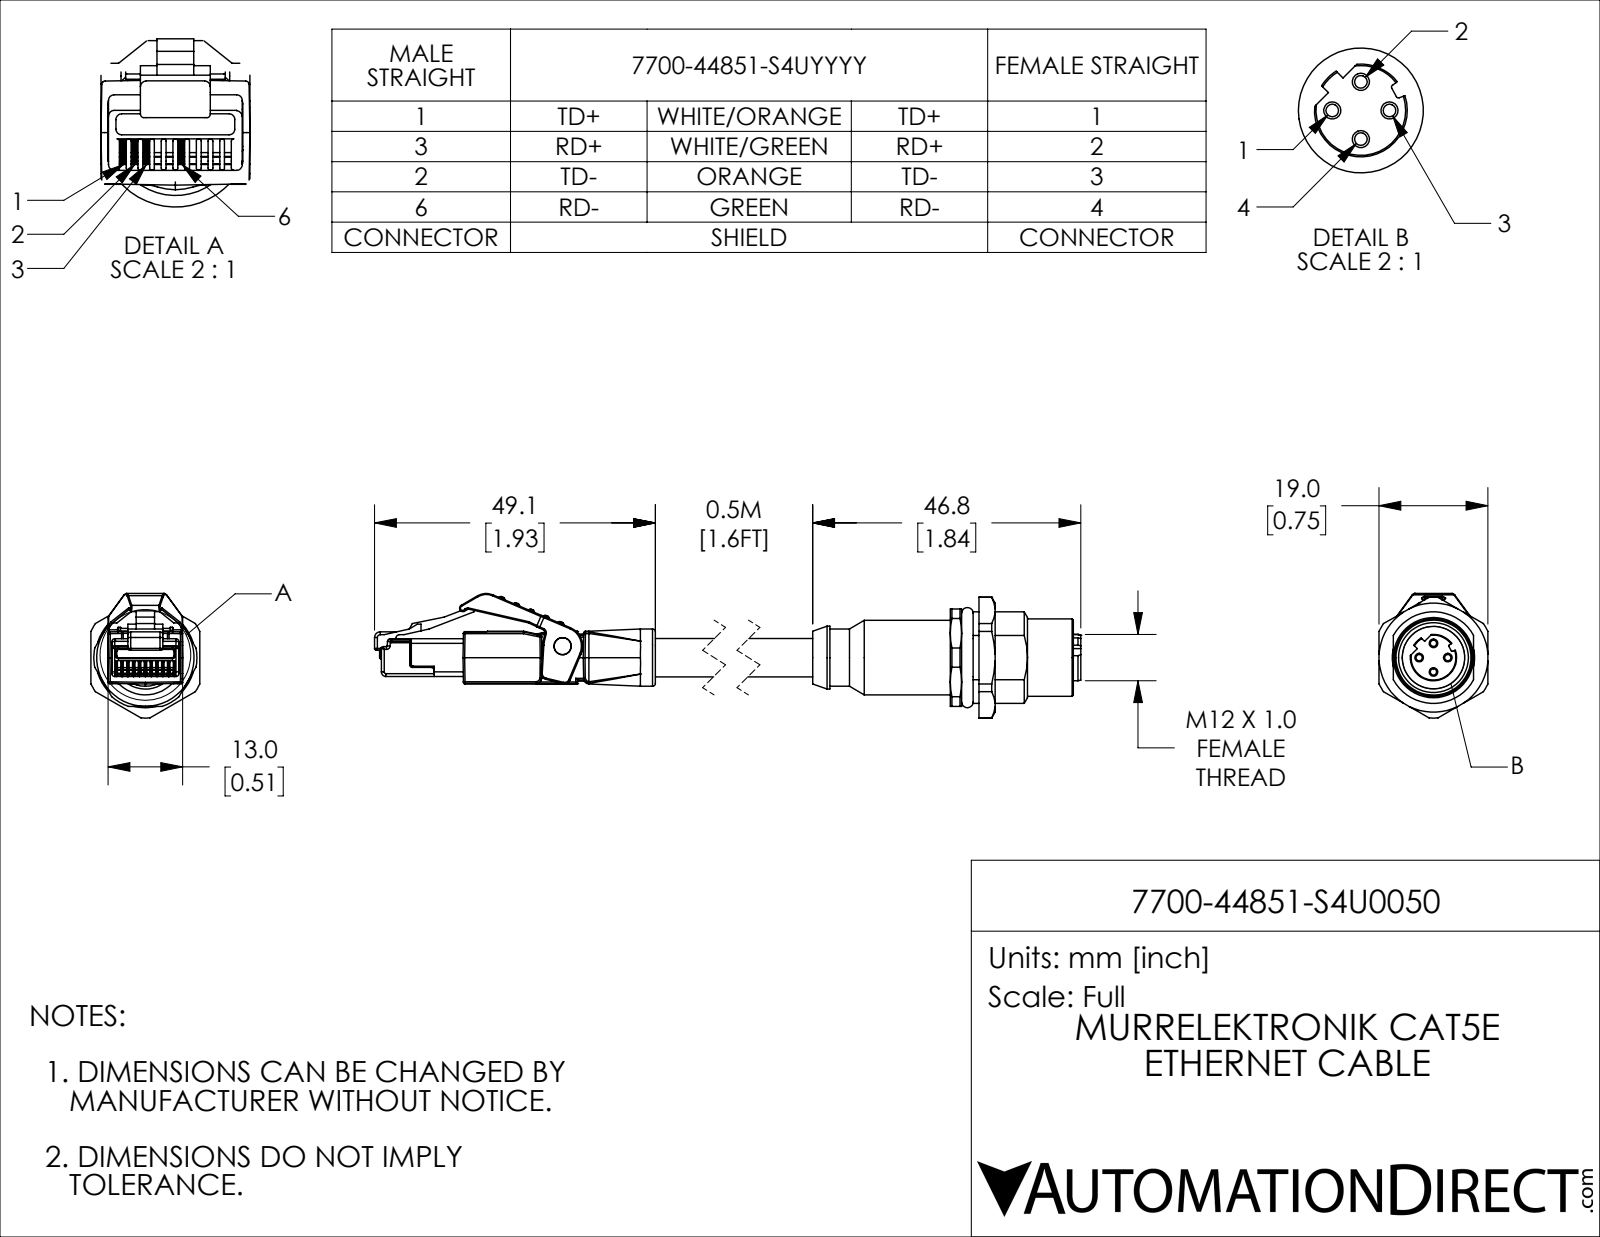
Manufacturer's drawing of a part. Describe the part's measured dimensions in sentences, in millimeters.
The part is named "7700-44851-S4U0050_NUT; 7700-44851-S4U0050_2; 7700-44851-S4U0050; 7700-44851-S4U0050_1". Its 3-D file was written by "SolidWorks 2021 (CONFIG_CONTROL_DESIGN)". It is 3 solids with 838 faces: 325 planar, 331 cylindrical and 182 other. Overall it measures 134.9 by 21.7 by 19 millimeters. Its volume is 13 000 cubic millimeters and its surface area 7 471 square millimeters. Round holes: 4 of diameter 1.1, 1 of diameter 3, 1 of diameter 10.9, 1 of diameter 12.2, 1 of diameter 14.4. Round bosses or shafts: 1 of diameter 13.5, 1 of diameter 13, 1 of diameter 11, 1 of diameter 10, 1 of diameter 6.7, 1 of diameter 3. Partial cylindrical surfaces (rounded edges, fillets, slot ends): 83 of radius 0.2, 64 of radius 0.3, 24 of radius 0.5, 20 of radius 0.1, 5 of radius 0.8, 5 of radius 1, 2 of radius 2, 2 of radius 5. The main face-to-face distances are 13, 9.2, 0.5, 13.5, 2.8, 5, 7.8, 1.1, 12.9, 0.6. The hole center spacings are 2.5, 3.5, 5.
